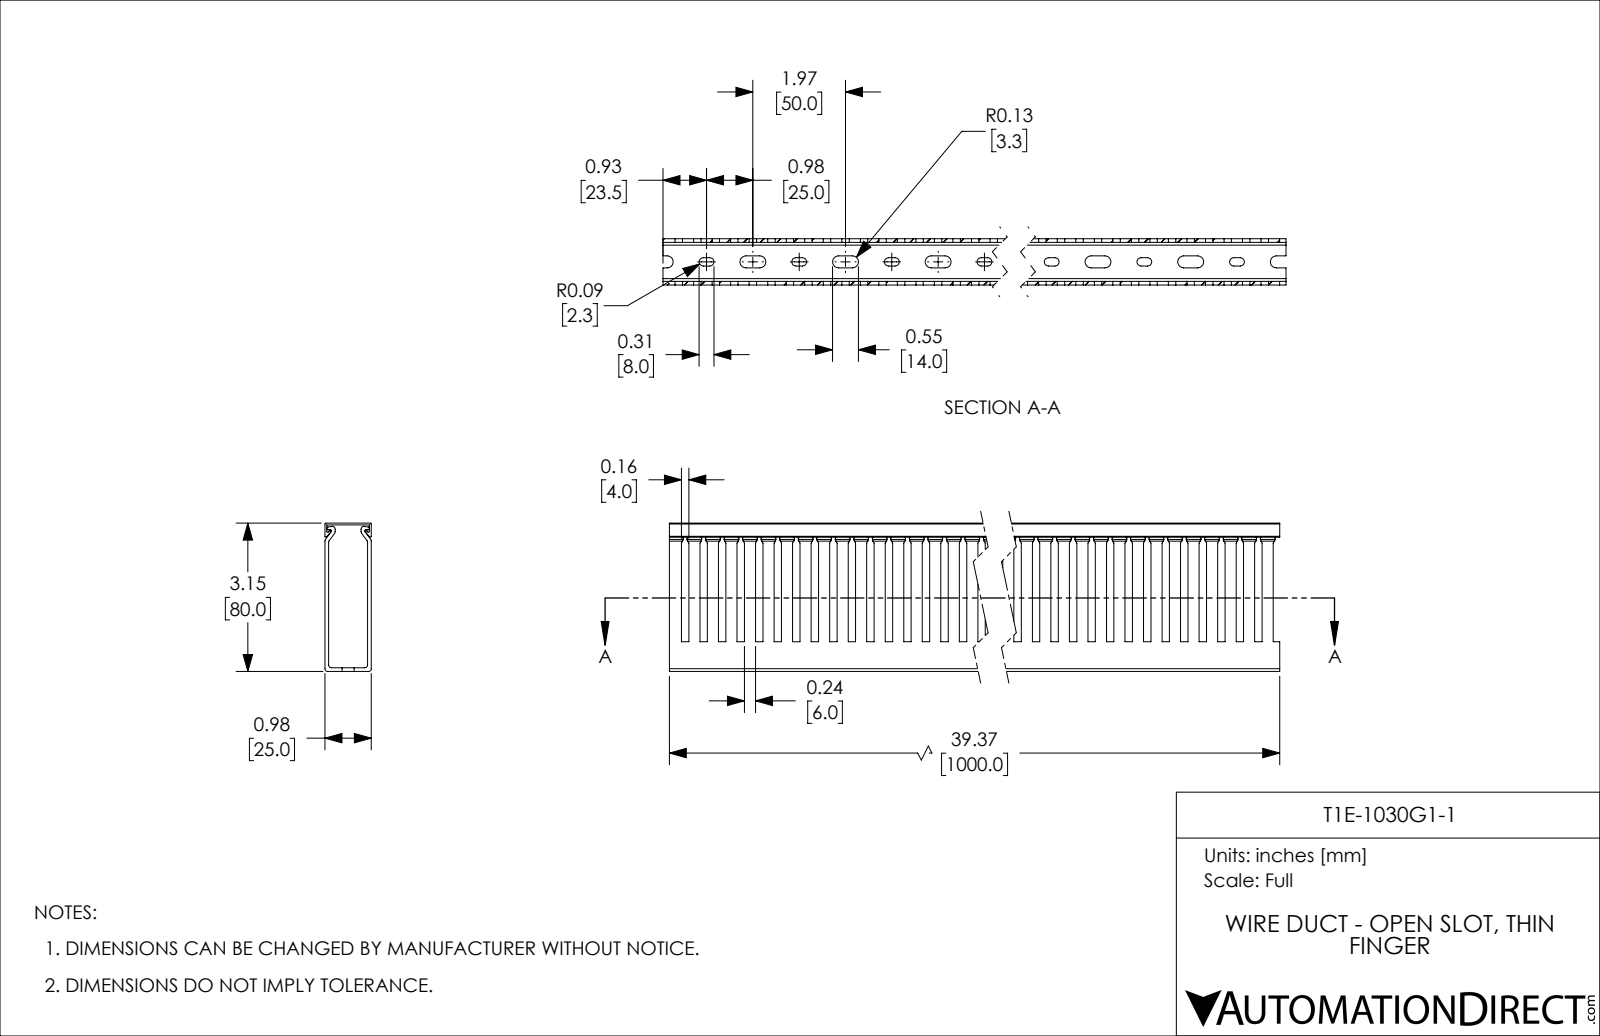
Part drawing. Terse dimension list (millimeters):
name: T1E-1030G1-1
written by: SolidWorks 2021 (CONFIG_CONTROL_DESIGN)
unit: mm
bodies: 2 solids, 745 faces (434 planar, 311 cylindrical, 0 other)
size: 1000 × 80 × 25
volume: 395 683 mm³; area: 445 171 mm²
rounds: 40× R2.25, 40× R3.25, 12× R1.5, 8× R0.5, 6× R0.75
face distances: 2, 23, 25, 21, 1, 80, 79, 77, 78, 24
